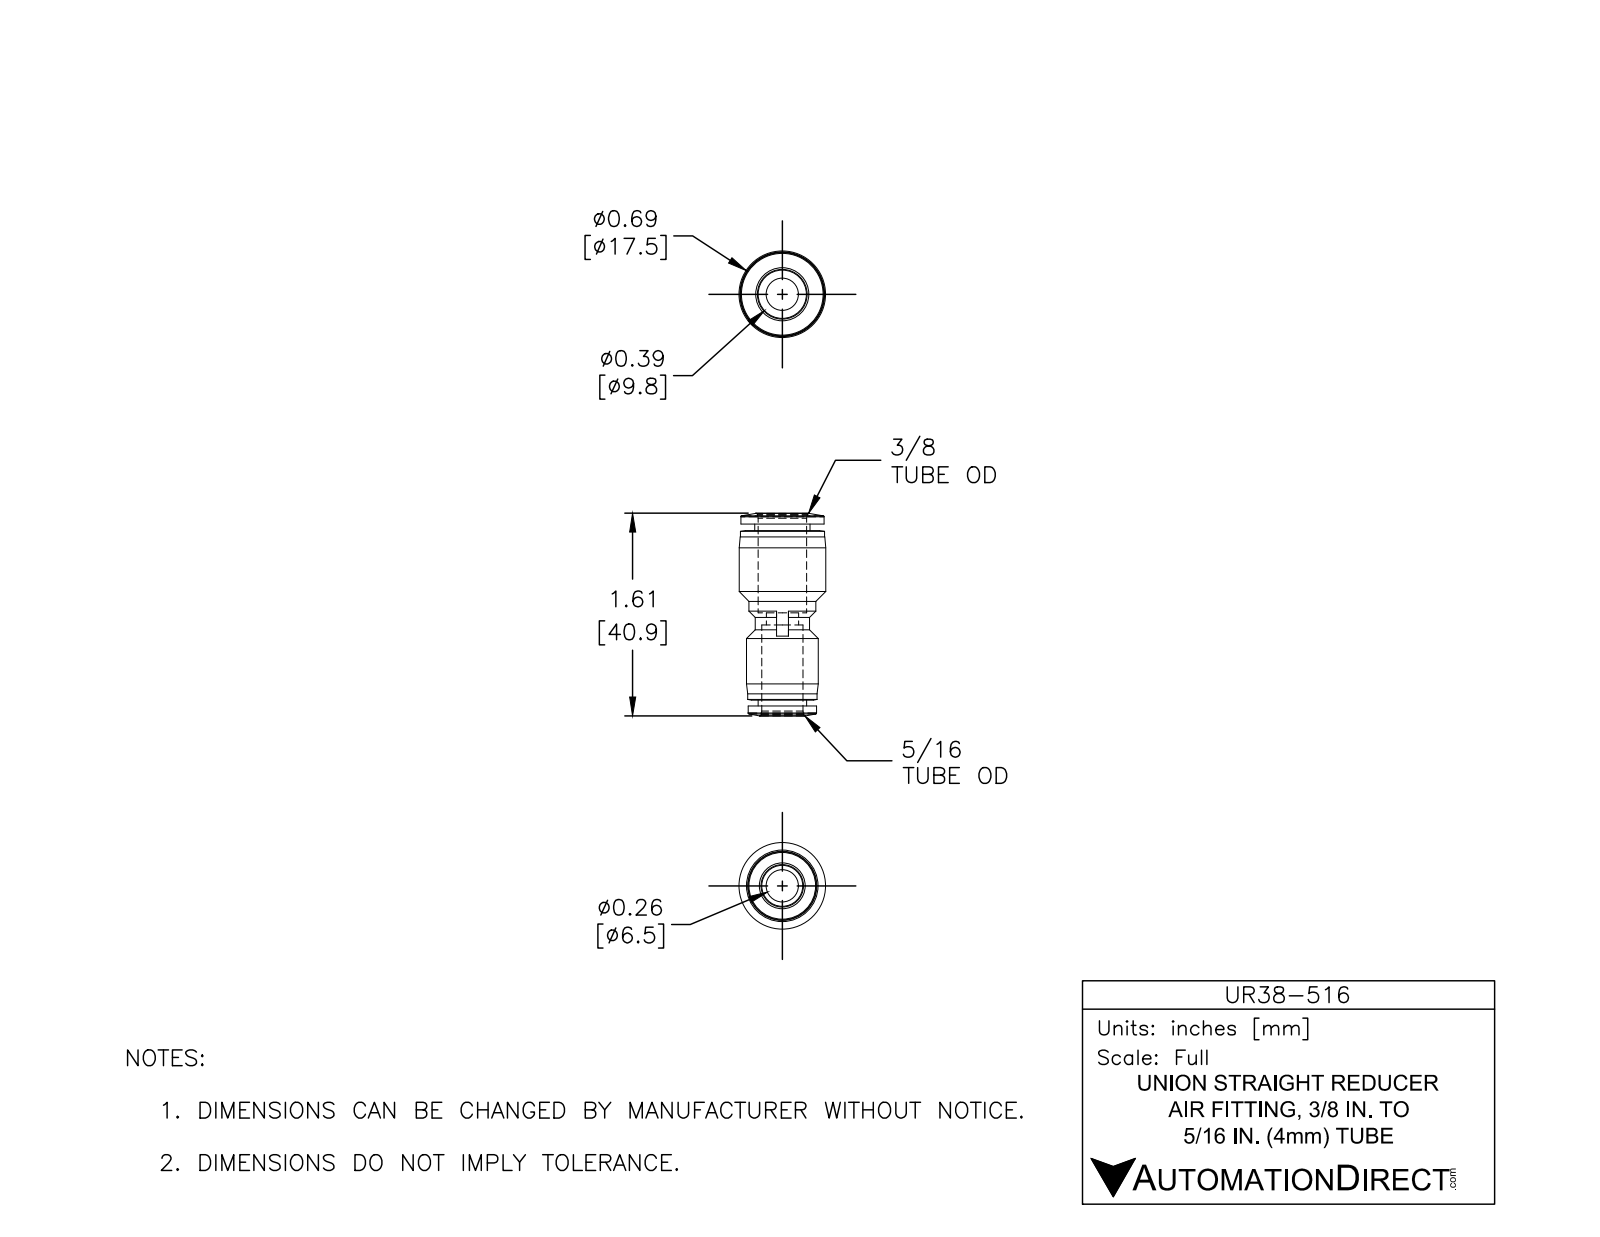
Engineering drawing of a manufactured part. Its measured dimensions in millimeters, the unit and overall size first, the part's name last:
Units: millimetres
Overall size (bounding box): 40.9 × 17.5 × 17.5
Round holes (diameter × count): ⌀6.5 ×1, ⌀8.3 ×1, ⌀9.8 ×1
Round bosses / shafts (diameter × count): ⌀17.5 ×1, ⌀17 ×1, ⌀16.8 ×1, ⌀14.5 ×1, ⌀14 ×1, ⌀13.8 ×1, ⌀13.5 ×1, ⌀11.2 ×1
Main face-to-face distances: 1.3, 35.5, 36.8, 1.2, 34.2, 35.6, 18.8, 17.7, 16.6, 17.9
Volume: 4 600 mm³ · Surface area: 3 799 mm²
Bodies: 1 solid, 67 faces (11 planar, 26 cylindrical, 30 other)
Part name (STEP PRODUCT): UR38-516
STEP written by: SolidWorks 2015 (CONFIG_CONTROL_DESIGN)
